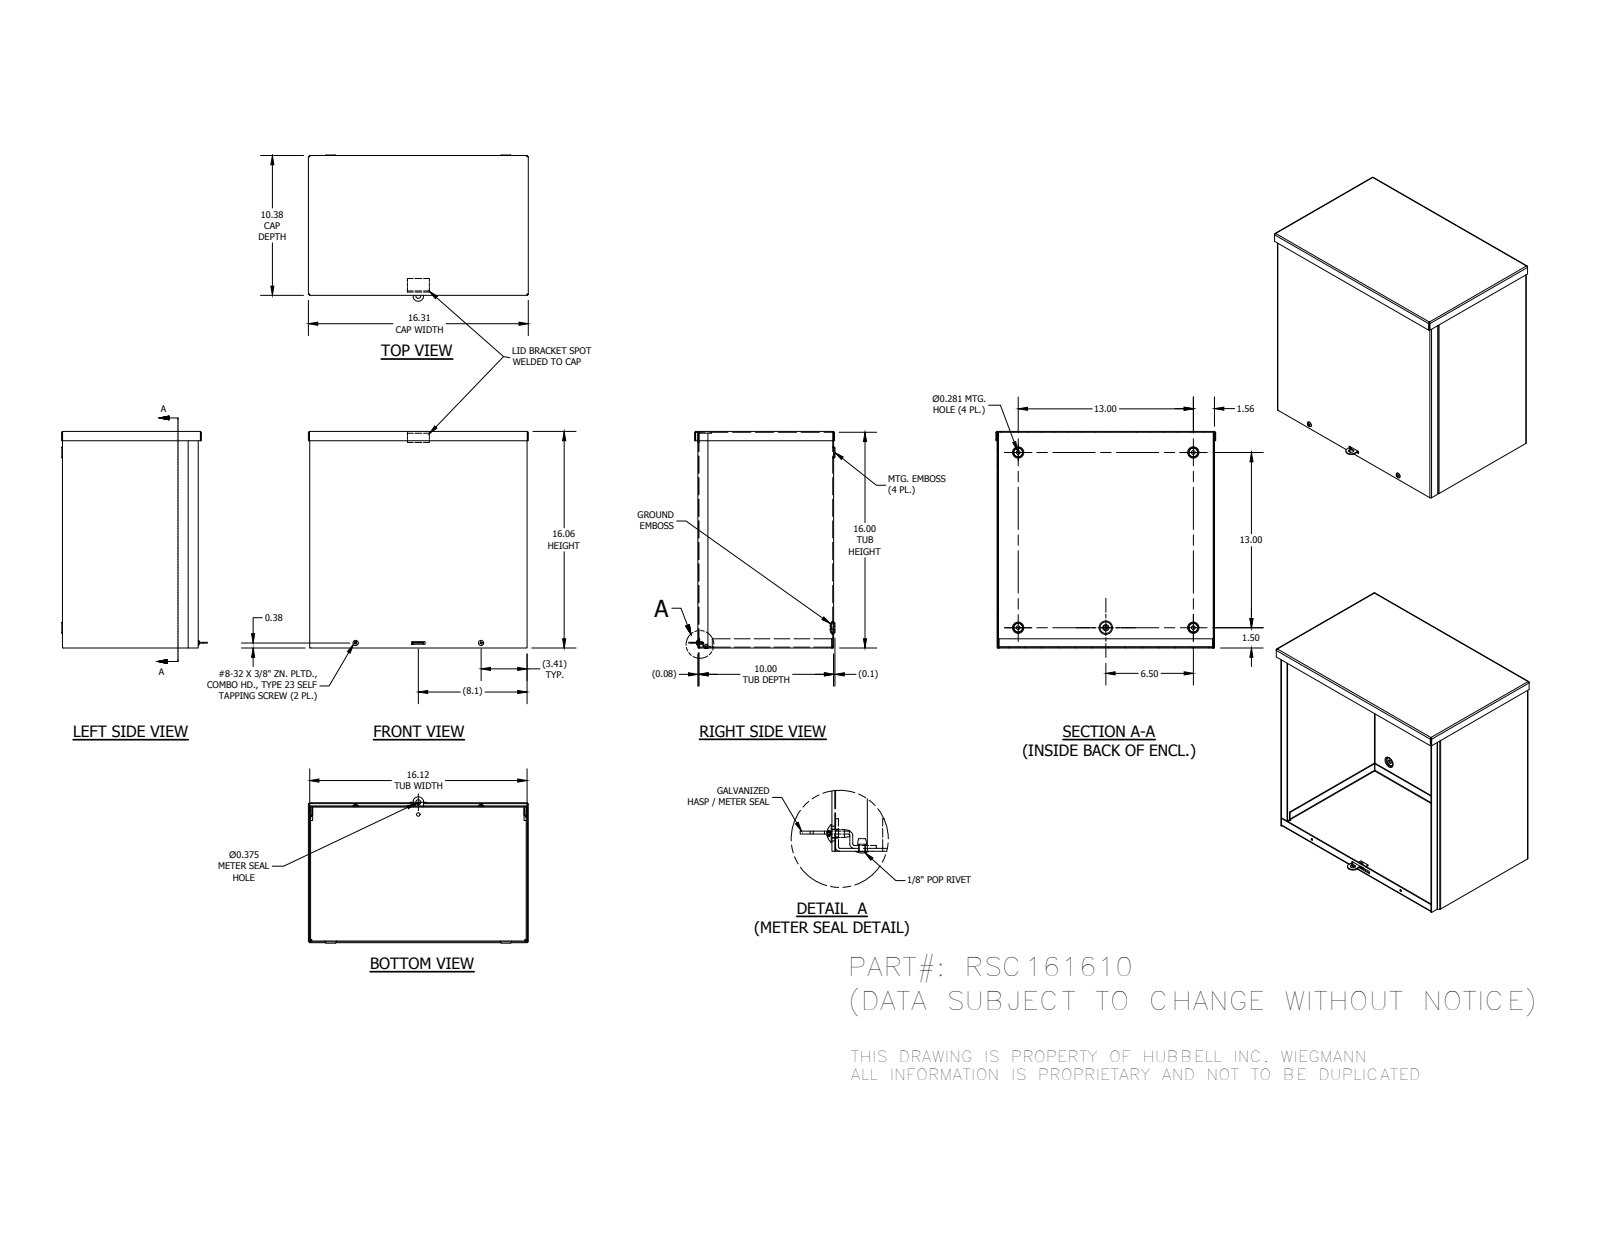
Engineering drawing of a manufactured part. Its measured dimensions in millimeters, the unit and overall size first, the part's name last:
Units: millimetres
Overall size (bounding box): 414.31 × 408.99 × 275.6
Round holes (diameter × count): ⌀7.14 ×4, ⌀7.94 ×4, ⌀3.73 ×2, ⌀3.17 ×1, ⌀3.45 ×1, ⌀4.34 ×1, ⌀9.52 ×1
Round bosses / shafts (diameter × count): ⌀9.75 ×2, ⌀4.17 ×2, ⌀6.65 ×1, ⌀5.93 ×1, ⌀3.17 ×1
Partial cylindrical surfaces — rounded edges, fillets, slot ends (radius × count): R0.79 ×19, R2.37 ×18, R2.67 ×1, R10.16 ×1
Main face-to-face distances: 1.57, 254.4, 406.4, 407.97, 255.97, 252.83, 404.83, 409.54, 1.58, 6.41
Hole centre spacings: 54.86, 284.81, 236.54, 121.67, 330.2, 361.82, 457.19, 165.1
Volume: 1 270 000 mm³ · Surface area: 1 625 000 mm²
Bodies: 9 solids, 320 faces (183 planar, 61 cylindrical, 76 other)
Part name (STEP PRODUCT): RSC161610BKPA; RSC1610EWPA; RSC1616LFA; RSC1610CPA (+5 more)
STEP written by: Autodesk Inventor 2014 (AUTOMOTIVE_DESIGN)
